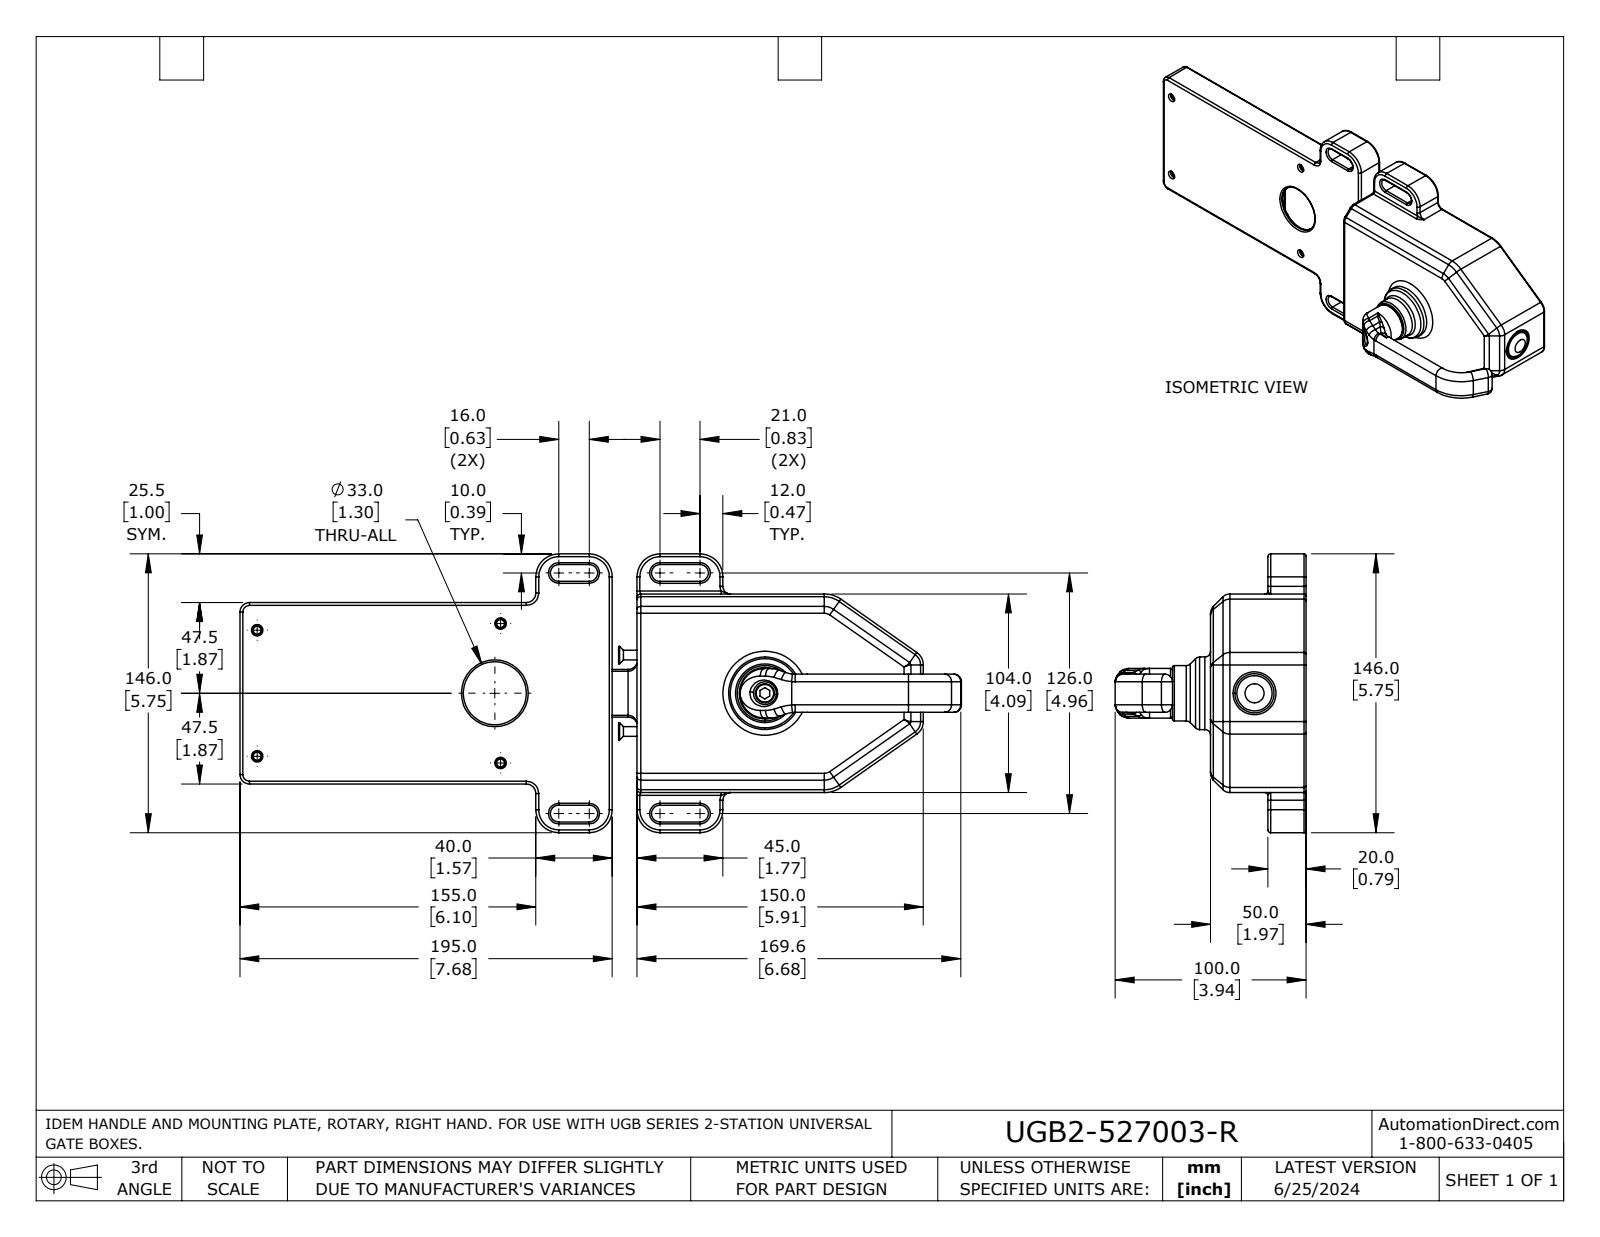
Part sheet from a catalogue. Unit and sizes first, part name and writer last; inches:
Units: inches
Overall size (bounding box): 14.882 × 5.748 × 3.937
Round holes (diameter × count): ⌀0.165 ×10, ⌀0.217 ×4, ⌀0.236 ×4, ⌀0.13 ×2, ⌀0.413 ×2, ⌀0.248 ×1, ⌀0.268 ×1, ⌀0.472 ×1, ⌀0.559 ×1, ⌀0.827 ×1, ⌀0.906 ×1, ⌀1.165 ×1
Round bosses / shafts (diameter × count): ⌀0.335 ×4, ⌀0.197 ×4, ⌀0.173 ×4, ⌀0.787 ×2, ⌀0.354 ×2, ⌀0.276 ×2, ⌀0.199 ×2, ⌀1.496 ×1
Partial cylindrical surfaces — rounded edges, fillets, slot ends (radius × count): R0.039 ×259, R0.079 ×90, R0.197 ×28, R0.118 ×24, R0.031 ×19, R0.02 ×12, R0.157 ×12, R0.059 ×11
Main face-to-face distances: 0.098, 0.65, 0.138, 0.039, 0.748, 1.929, 1.831, 0.551, 1.693, 1.28
Hole centre spacings: 0.812, 1.442, 1.562, 2.195, 2.665, 3.295, 3.645, 3.744
Volume: 28.11 in³ · Surface area: 340.3 in²
Bodies: 6 solids, 1652 faces (379 planar, 654 cylindrical, 619 other)
Part name (STEP PRODUCT): UGB2-527003-R
STEP written by: SolidWorks 2023 (AUTOMOTIVE_DESIGN)
